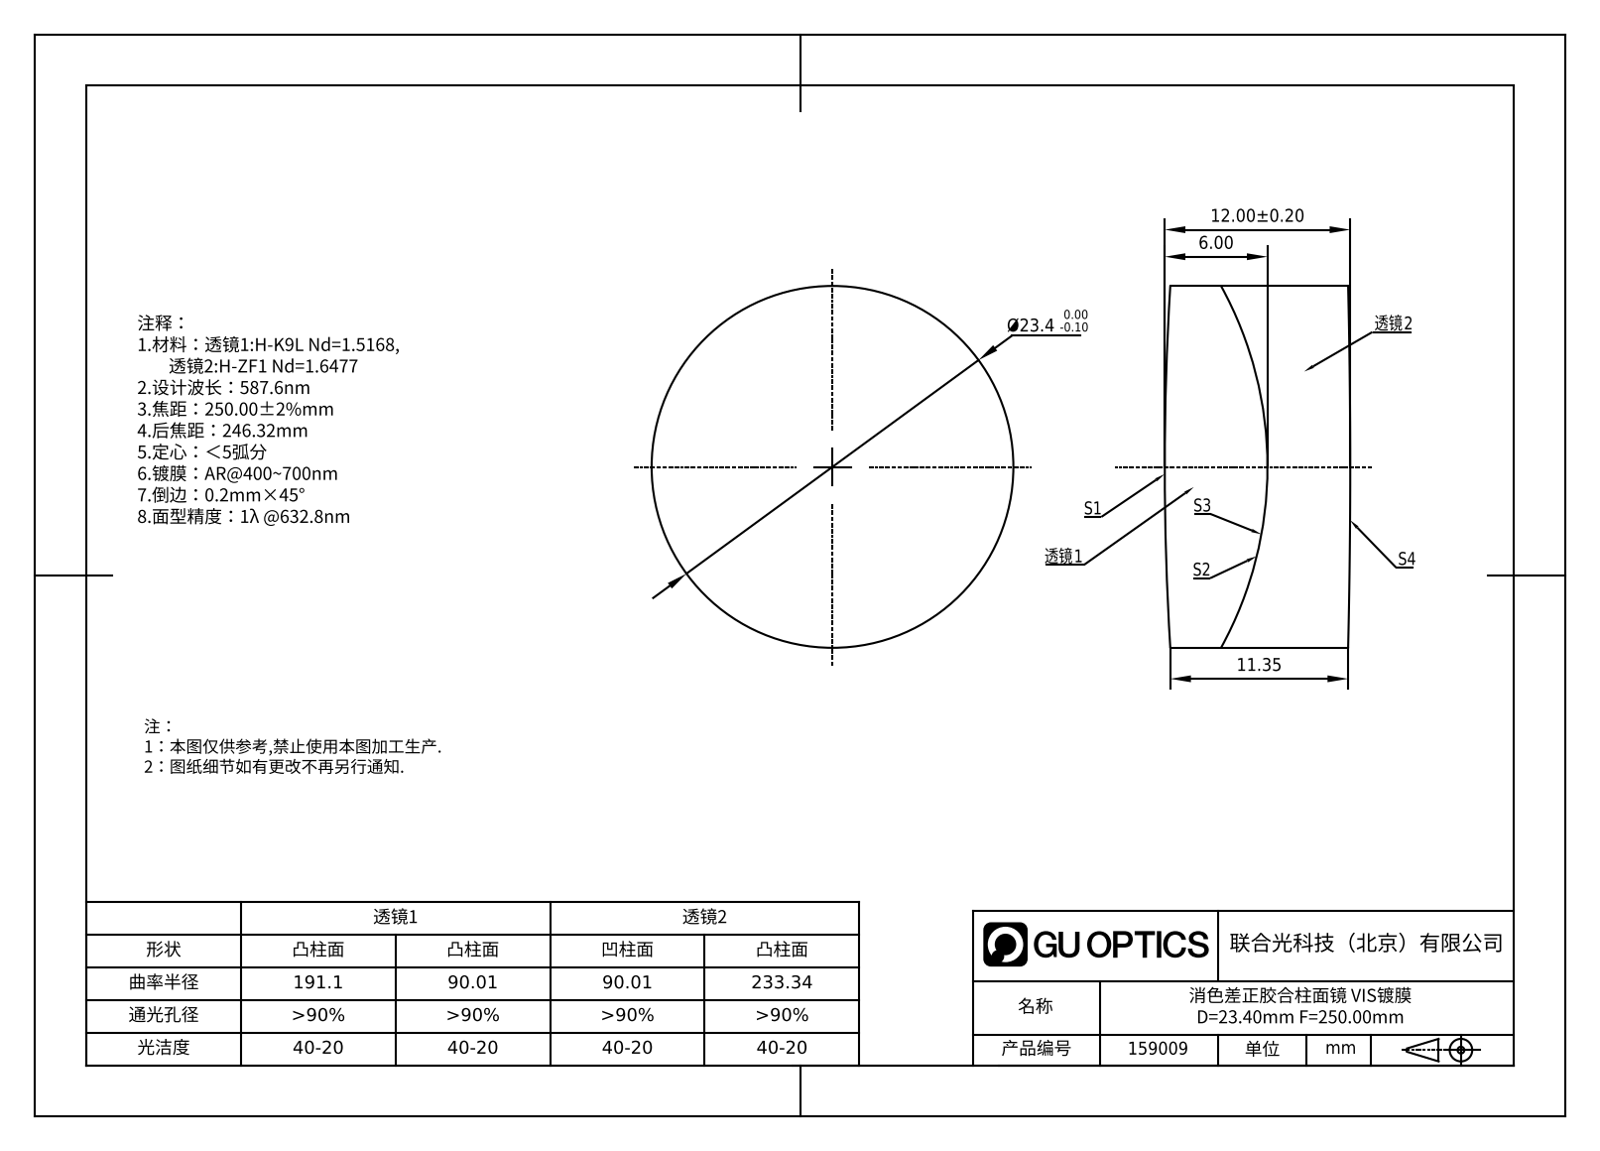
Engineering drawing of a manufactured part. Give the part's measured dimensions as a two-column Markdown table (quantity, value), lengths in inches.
| quantity | value |
| --- | --- |
| part name | 159009 |
| STEP written by | SolidWorks 2020 (CONFIG_CONTROL_DESIGN) |
| units | inches |
| bodies | 1 solid, 5 faces (0 planar, 5 cylindrical, 0 other) |
| overall size | 0.921 × 0.921 × 0.472 |
| volume | 0.312 in³ |
| surface area | 2.672 in² |
| round bosses / shafts (diameter × count) | 0.921 × 1 |
| partial cylindrical surfaces (radius × count) | 7.524 × 1, 19.515 × 1 |
